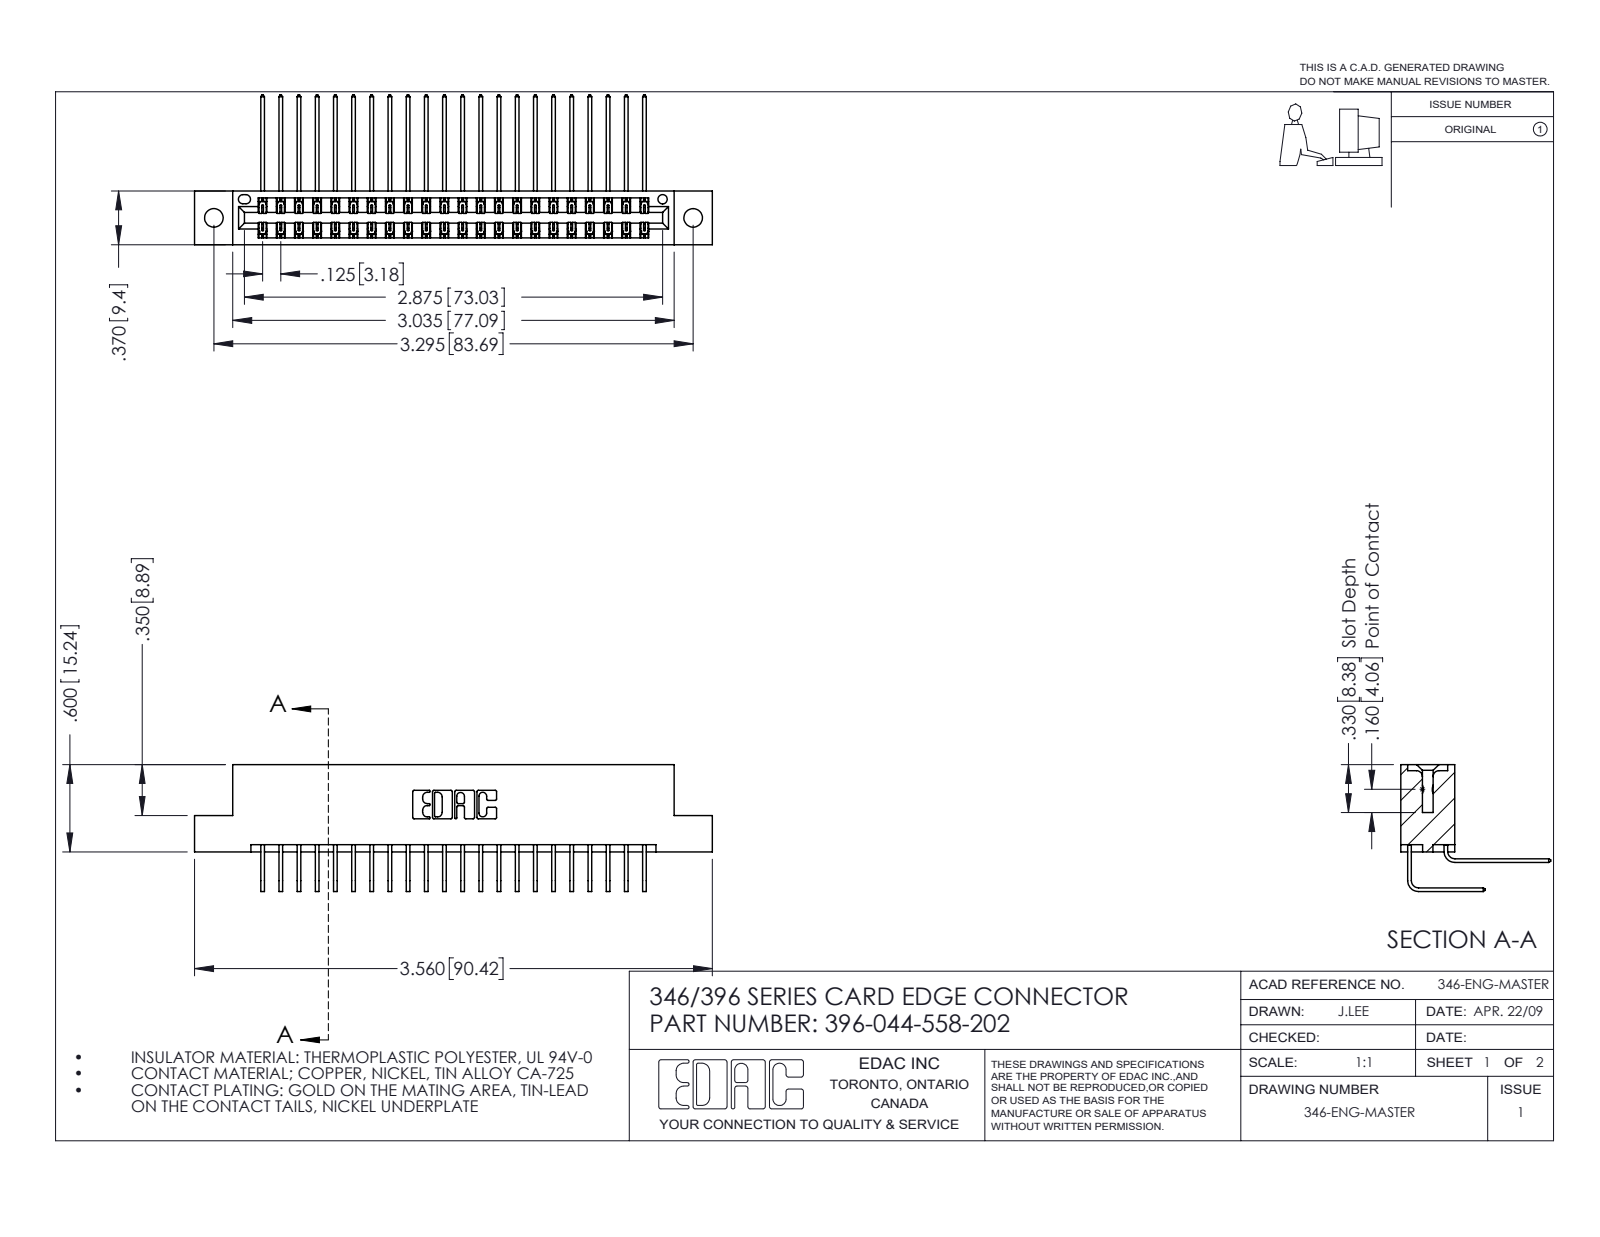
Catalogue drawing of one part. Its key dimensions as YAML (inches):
part_name: "396-044-558-202; 345-292-001_558 Tail - 2; 345-292-001_558 559 Tail - 1; 346 Part_Flush Mounting Lugs - 0.128 Dia"
step_written_by: "SolidWorks 2016 (CONFIG_CONTROL_DESIGN)"
units: inches
bodies: {solids: 45, faces: 2498, planar: 1704, cylindrical: 794, other: 0}
overall_size: [3.56, 1.03, 0.873]
volume: 0.542
surface_area: 19.9
round_holes:
  - {diameter: 0.128, count: 2}
  - {diameter: 0.064, count: 1}
partial_cylinders:
  - {radius: 0.006, count: 66}
  - {radius: 0.01, count: 22}
  - {radius: 0.007, count: 6}
  - {radius: 0.031, count: 6}
  - {radius: 0.026, count: 3}
  - {radius: 0.014, count: 2}
  - {radius: 0.022, count: 2}
  - {radius: 0.024, count: 2}
face_to_face_distances: [0.322, 0.048, 0.25, 0.025, 0.37, 0.298, 0.072, 0.275, 0.148, 0.222]
hole_center_spacings: [0.246, 3.087, 3.295]
